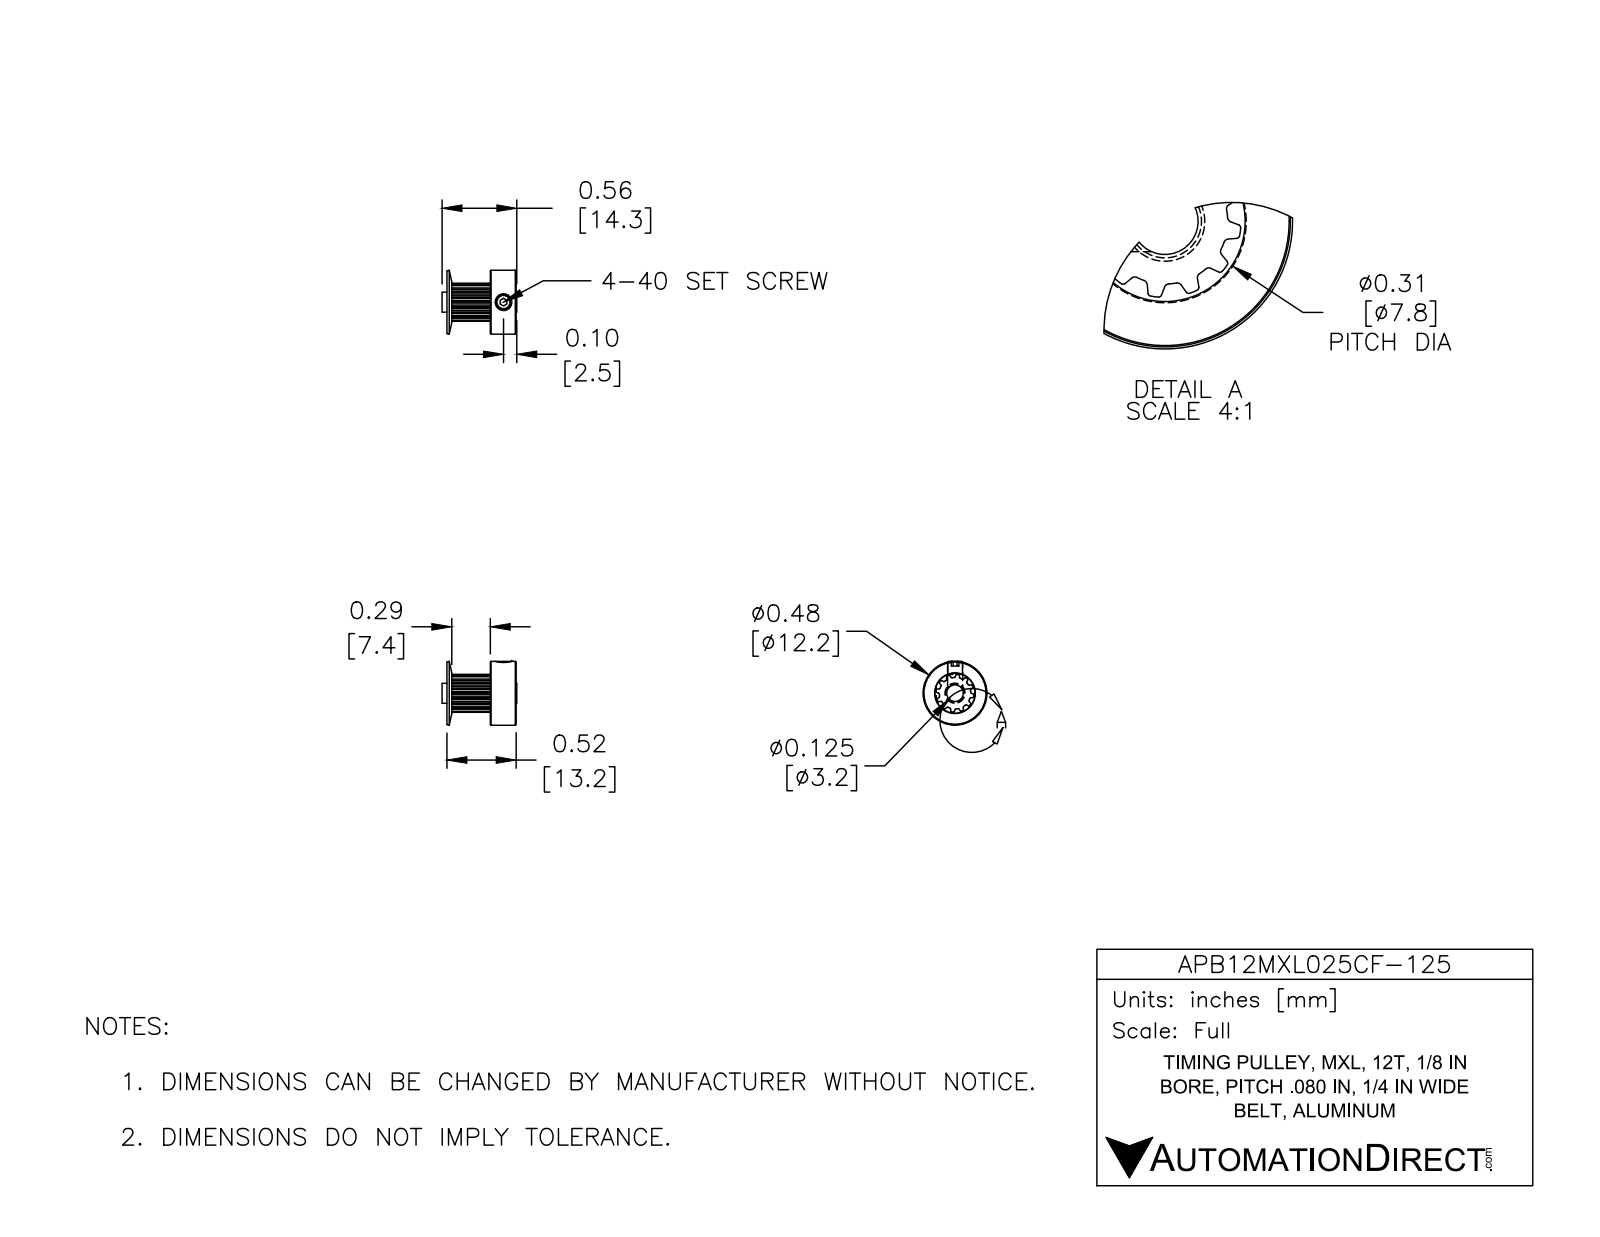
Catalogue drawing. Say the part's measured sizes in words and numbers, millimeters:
The part is named "APB12MXL025CF-125". Its 3-D file was written by "SolidWorks 2016 (AUTOMOTIVE_DESIGN)". It is 2 solids with 150 faces: 39 planar, 93 cylindrical and 18 other. Overall it measures 14.3 by 12.2 by 12.2 millimeters. Its volume is 770 cubic millimeters and its surface area 1 026 square millimeters. Round holes: 1 of diameter 2.9, 1 of diameter 3.2. Round bosses or shafts: 1 of diameter 12.2, 1 of diameter 3.8, 1 of diameter 2.8. Partial cylindrical surfaces (rounded edges, fillets, slot ends): 24 of radius 0.1, 24 of radius 0.2, 1 of radius 3, 1 of radius 3.6. The main face-to-face distances are 4.9, 7.8, 12.8, 2.2, 0.5, 7.4, 12.3, 2.2, 2.5, 1.3.
